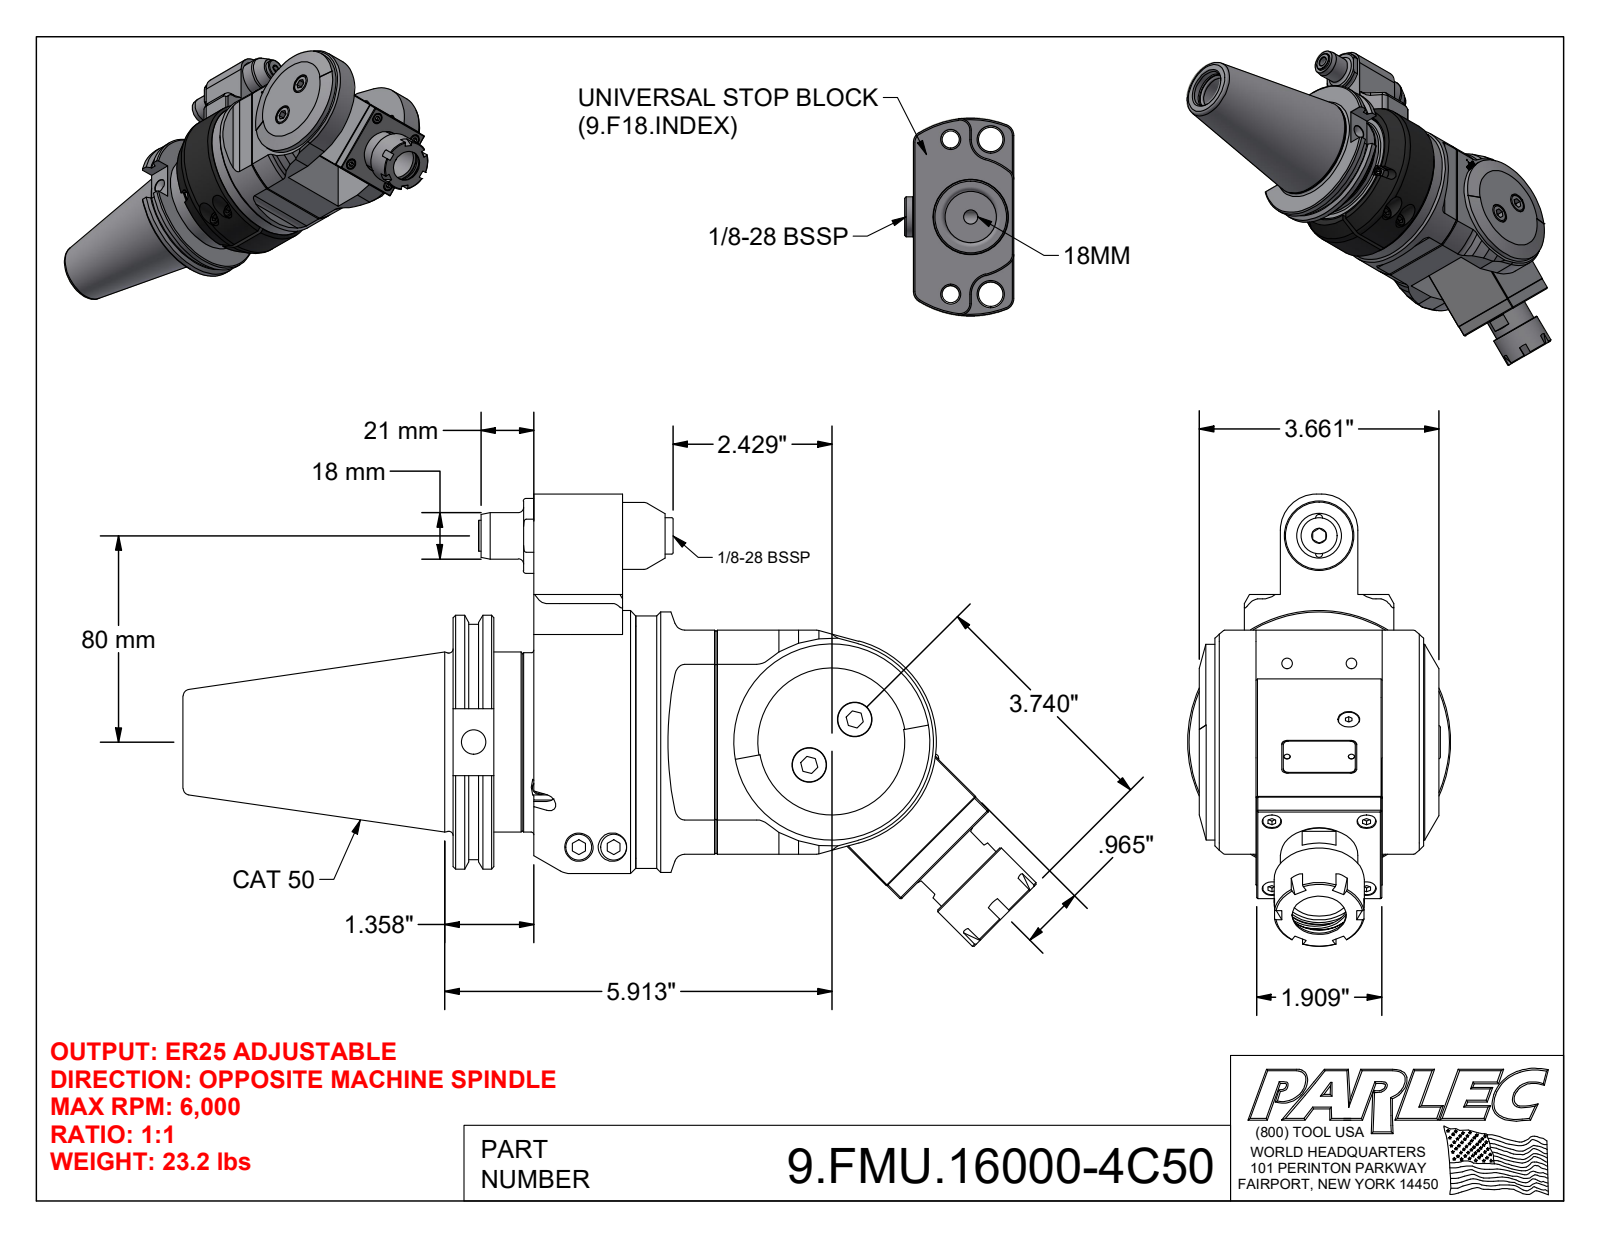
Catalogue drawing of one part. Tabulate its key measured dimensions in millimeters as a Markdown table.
| quantity | value |
| --- | --- |
| part name | 9.FMU.16000-4C50; 9FL1ATC; 9F18T180_ASM; 9F18T180A (+5 more) |
| STEP written by | Autodesk Inventor 2025 (AUTOMOTIVE_DESIGN) |
| units | millimeters |
| bodies | 6 solids, 646 faces (360 planar, 135 cylindrical, 151 other) |
| overall size | 331 × 175.45 × 102 |
| volume | 1 538 000 mm³ |
| surface area | 216 149 mm² |
| round holes (diameter × count) | 7.5 × 4, 13.5 × 3, 2.6 × 2, 4 × 2, 5 × 2, 8.5 × 2, 10.4 × 2, 11 × 2, 27 × 2, 2.5 × 1, 3 × 1, 6.5 × 1 |
| round bosses / shafts (diameter × count) | 6 × 6, 10 × 4, 7 × 4, 13 × 3, 8 × 3, 18 × 2, 2.5 × 2, 102 × 1 |
| partial cylindrical surfaces (radius × count) | 2 × 8, 4 × 6, 0.5 × 2, 1 × 2, 3.5 × 2, 5 × 2, 14 × 2, 11 × 1 |
| main face-to-face distances | 14, 63, 49, 77, 8, 32, 87, 22, 71, 85 |
| hole center spacings | 26, 1.5, 7, 12.5, 24.96, 25, 27.08, 32.96 |
